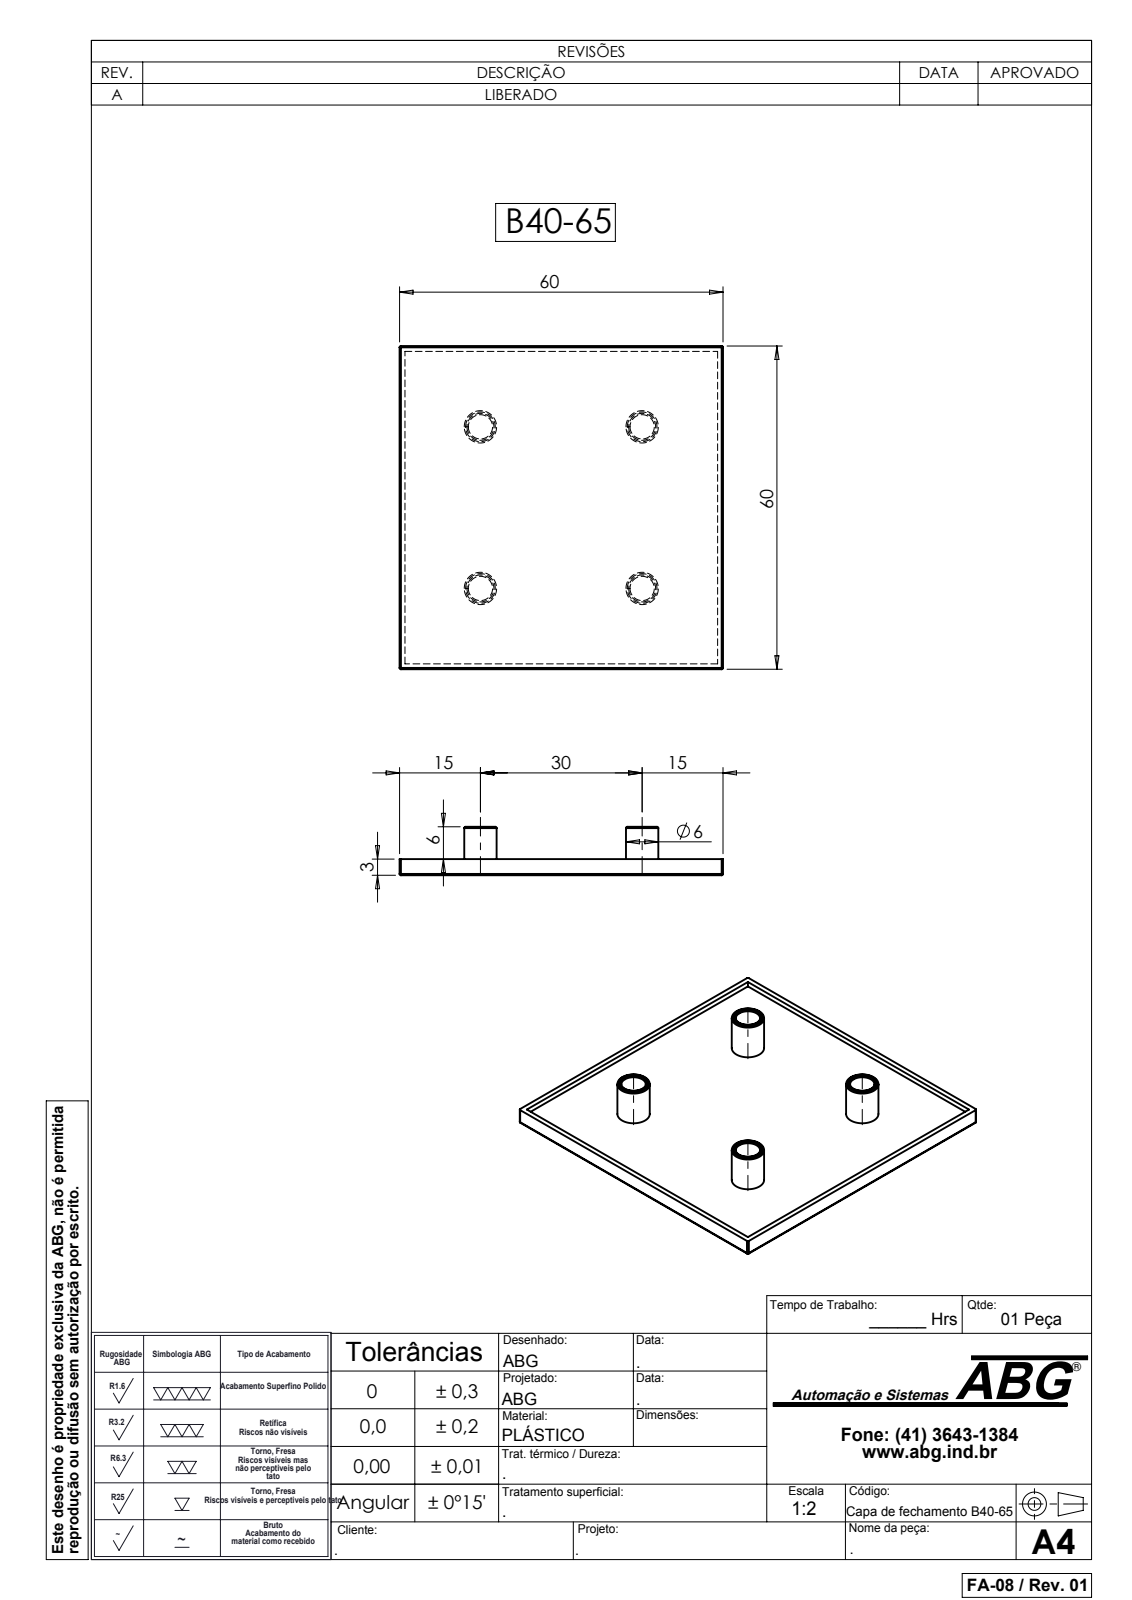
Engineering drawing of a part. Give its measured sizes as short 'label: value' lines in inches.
name: B40-65
written by: SolidWorks 2007 (CONFIG_CONTROL_DESIGN)
unit: in
bodies: 1 solid, 63 faces (19 planar, 24 cylindrical, 20 other)
size: 2.362 × 2.362 × 0.354
volume: 0.475 in³; area: 14 in²
holes: 4× ⌀0.177
bosses: 4× ⌀0.236
rounds: 8× R0.01
face distances: 0.079, 0.039, 2.362, 0.118, 2.323, 2.283, 0.354, 0.276, 0.236
hole spacings: 1.181, 1.67
